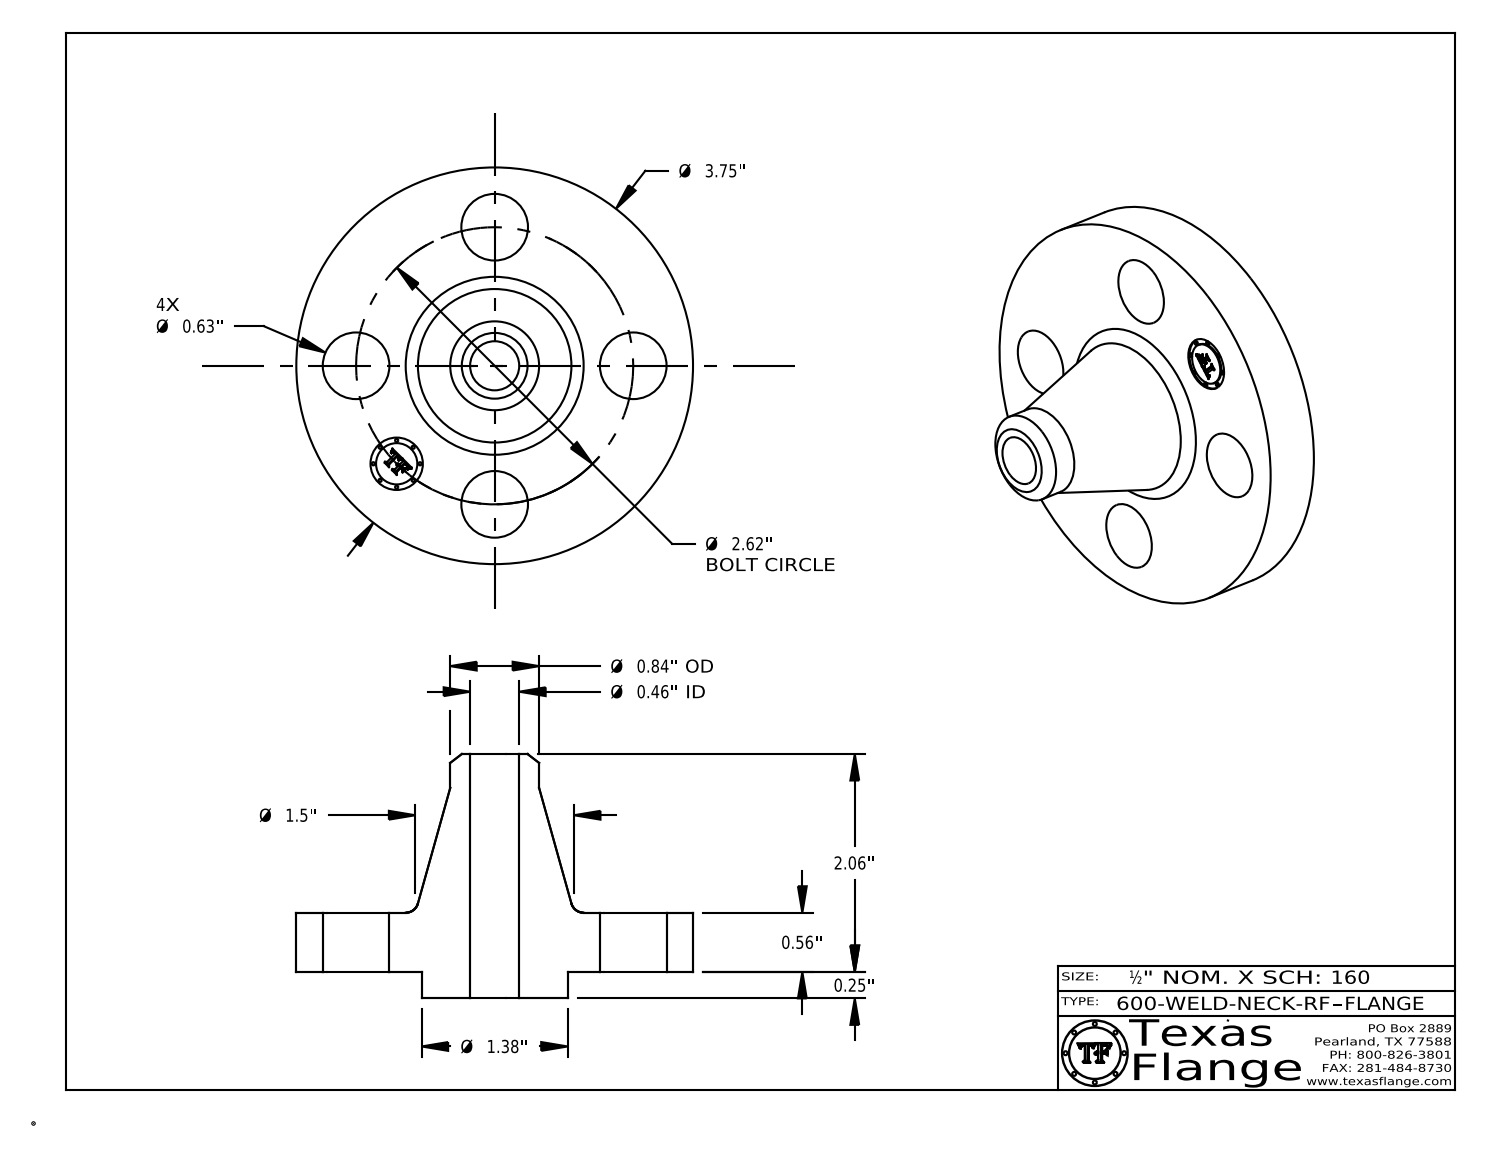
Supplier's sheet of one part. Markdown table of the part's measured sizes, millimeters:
| quantity | value |
| --- | --- |
| part name | 600-WELD-NECK-RF |
| STEP written by | CATIA V5 STEP AP214 (AUTOMOTIVE_DESIGN) |
| units | millimeters |
| bodies | 1 solid, 411 faces (369 planar, 36 cylindrical, 6 other) |
| overall size | 95.3 × 95.3 × 58.7 |
| volume | 113 800 mm³ |
| surface area | 24 960 mm² |
| round holes (diameter × count) | 16 × 4, 11.8 × 1, 12.6 × 1 |
| round bosses / shafts (diameter × count) | 0.8 × 8, 95.3 × 1, 35.1 × 1, 21.3 × 1, 9.9 × 1 |
| main face-to-face distances | 14.2, 6.4, 20.6, 58.7, 52.3, 38.1, 20.2, 13.8, 0.4, 38.5 |
| hole center spacings | 33.3, 47, 25.5, 61.5, 66.5, 33.3 |
